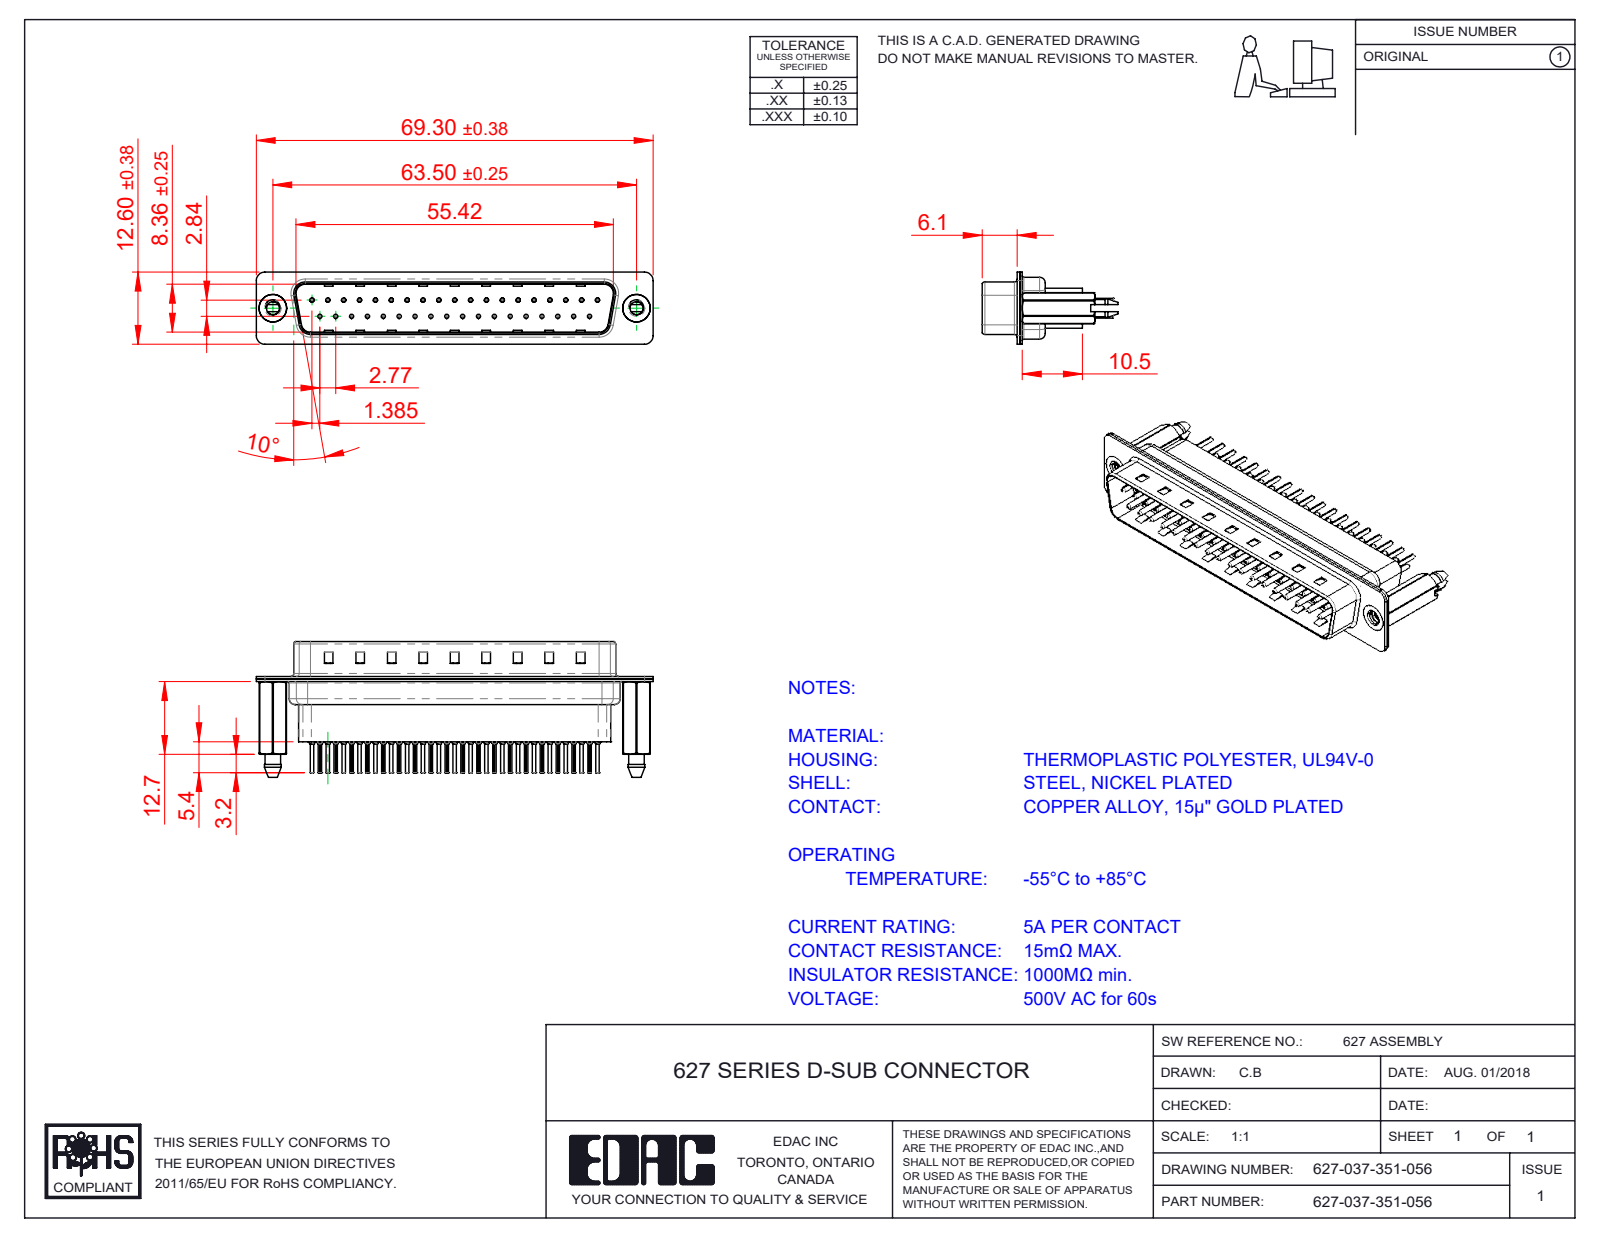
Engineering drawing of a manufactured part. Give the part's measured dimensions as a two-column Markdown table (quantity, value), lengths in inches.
| quantity | value |
| --- | --- |
| part name | 627 Shell Front_37 Contacts; 627 Contact Row 2_41; 627 4-40 Threaded Boardlock_HP51; 627 Housing_37 HP (+3 more) |
| STEP written by | SolidWorks 2020 (CONFIG_CONTROL_DESIGN) |
| units | inches |
| bodies | 42 solids, 4146 faces (1123 planar, 1576 cylindrical, 1447 other) |
| overall size | 2.728 × 0.929 × 0.496 |
| volume | 0.344 in³ |
| surface area | 22.39 in² |
| round holes (diameter × count) | 0.008 × 37, 0.014 × 37, 0.043 × 37, 0.063 × 37, 0.089 × 2, 0.157 × 2, 0.189 × 2 |
| round bosses / shafts (diameter × count) | 0.079 × 37, 0.059 × 37, 0.03 × 37, 0.024 × 37, 0.193 × 2 |
| partial cylindrical surfaces (radius × count) | 0.004 × 74, 0.059 × 18, 0.079 × 12, 0.063 × 10, 0.02 × 8, 0.01 × 4, 0.024 × 4, 0.026 × 4 |
| main face-to-face distances | 0.016, 0.032, 0.377, 0.027, 0.302, 0.018, 0.059, 0.043, 0.318, 0.345 |
| hole center spacings | 0.124, 0.109, 0.218, 0.327, 0.198, 0.398, 0.436, 0.503 |
